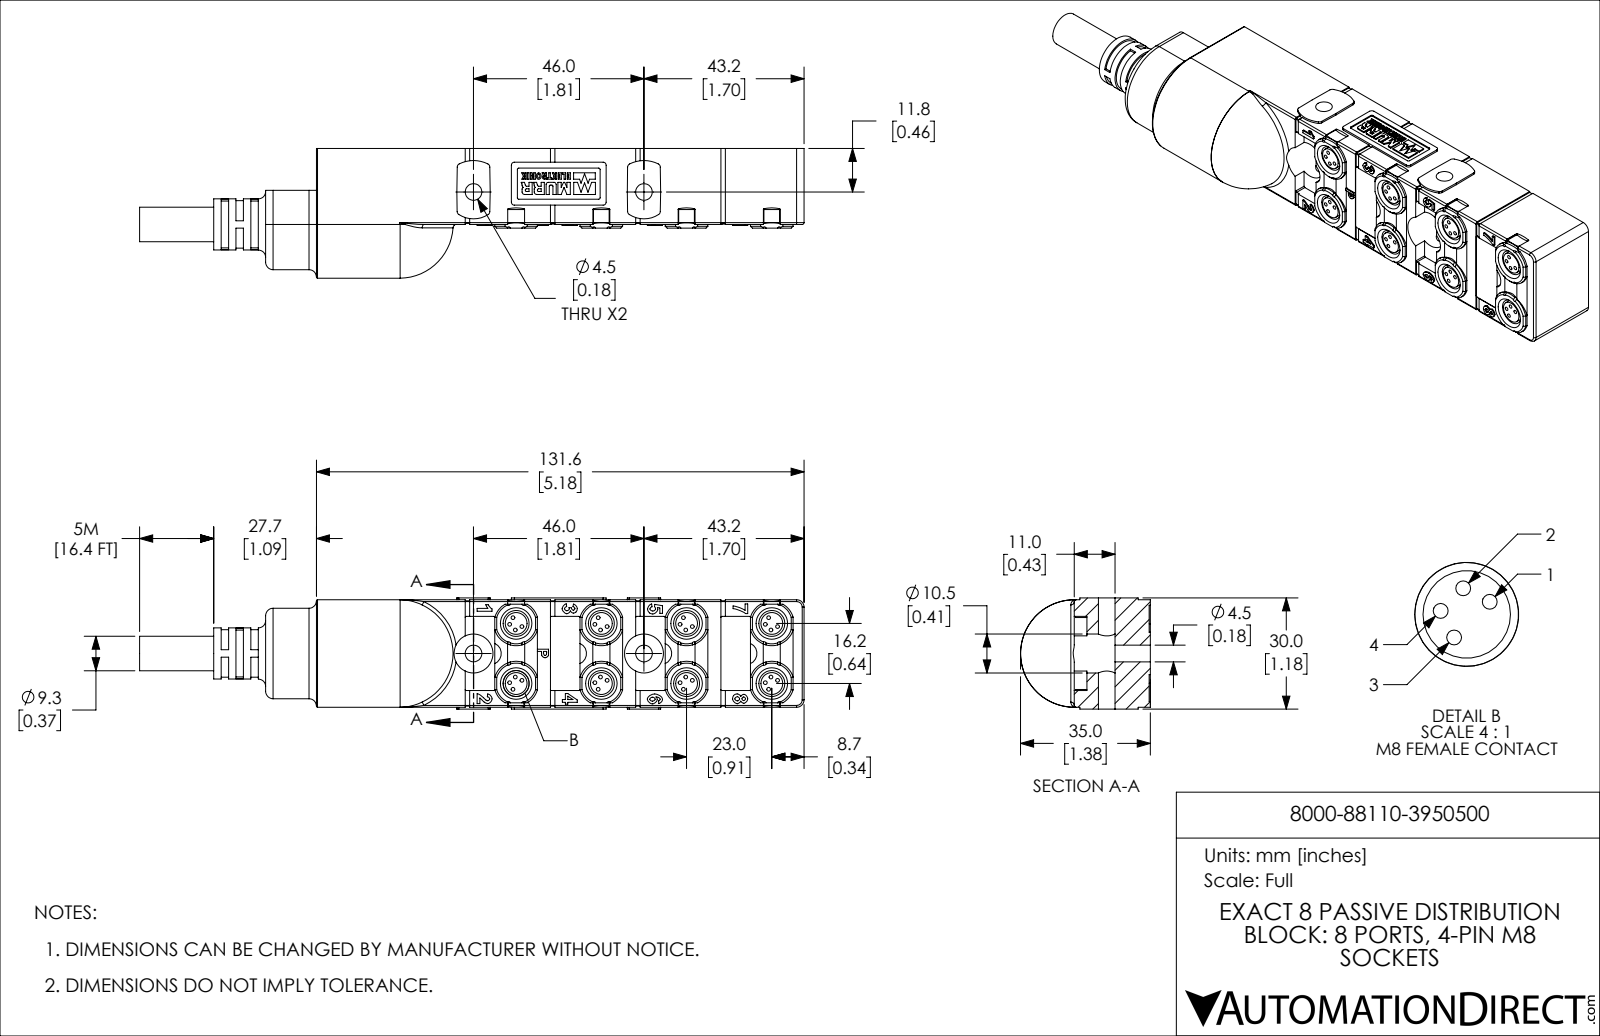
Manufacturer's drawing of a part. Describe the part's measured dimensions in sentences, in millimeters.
The part is named "8000-88110-3950500". Its 3-D file was written by "SolidWorks 2019 (CONFIG_CONTROL_DESIGN)". It is 1 solid with 1330 faces: 686 planar, 445 cylindrical and 199 other. Overall it measures 179.3 by 35 by 30 millimeters. Its volume is 94 650 cubic millimeters and its surface area 21 070 square millimeters. Round holes: 32 of diameter 1, 8 of diameter 7, 4 of diameter 4.5, 2 of diameter 10.5. Round bosses or shafts: 8 of diameter 5.9, 2 of diameter 11.4, 1 of diameter 13.8, 1 of diameter 12.8, 1 of diameter 9.3. Partial cylindrical surfaces (rounded edges, fillets, slot ends): 35 of radius 0.5, 24 of radius 0.2, 18 of radius 0.3, 12 of radius 10, 8 of radius 1, 8 of radius 6, 6 of radius 2, 4 of radius 0.3. The main face-to-face distances are 29, 20.5, 0.5, 29.5, 20.2, 11, 11.3, 9.2, 30, 9.5. The hole center spacings are 1.8, 2, 3.4, 46, 69, 23, 13.7, 14.5.
